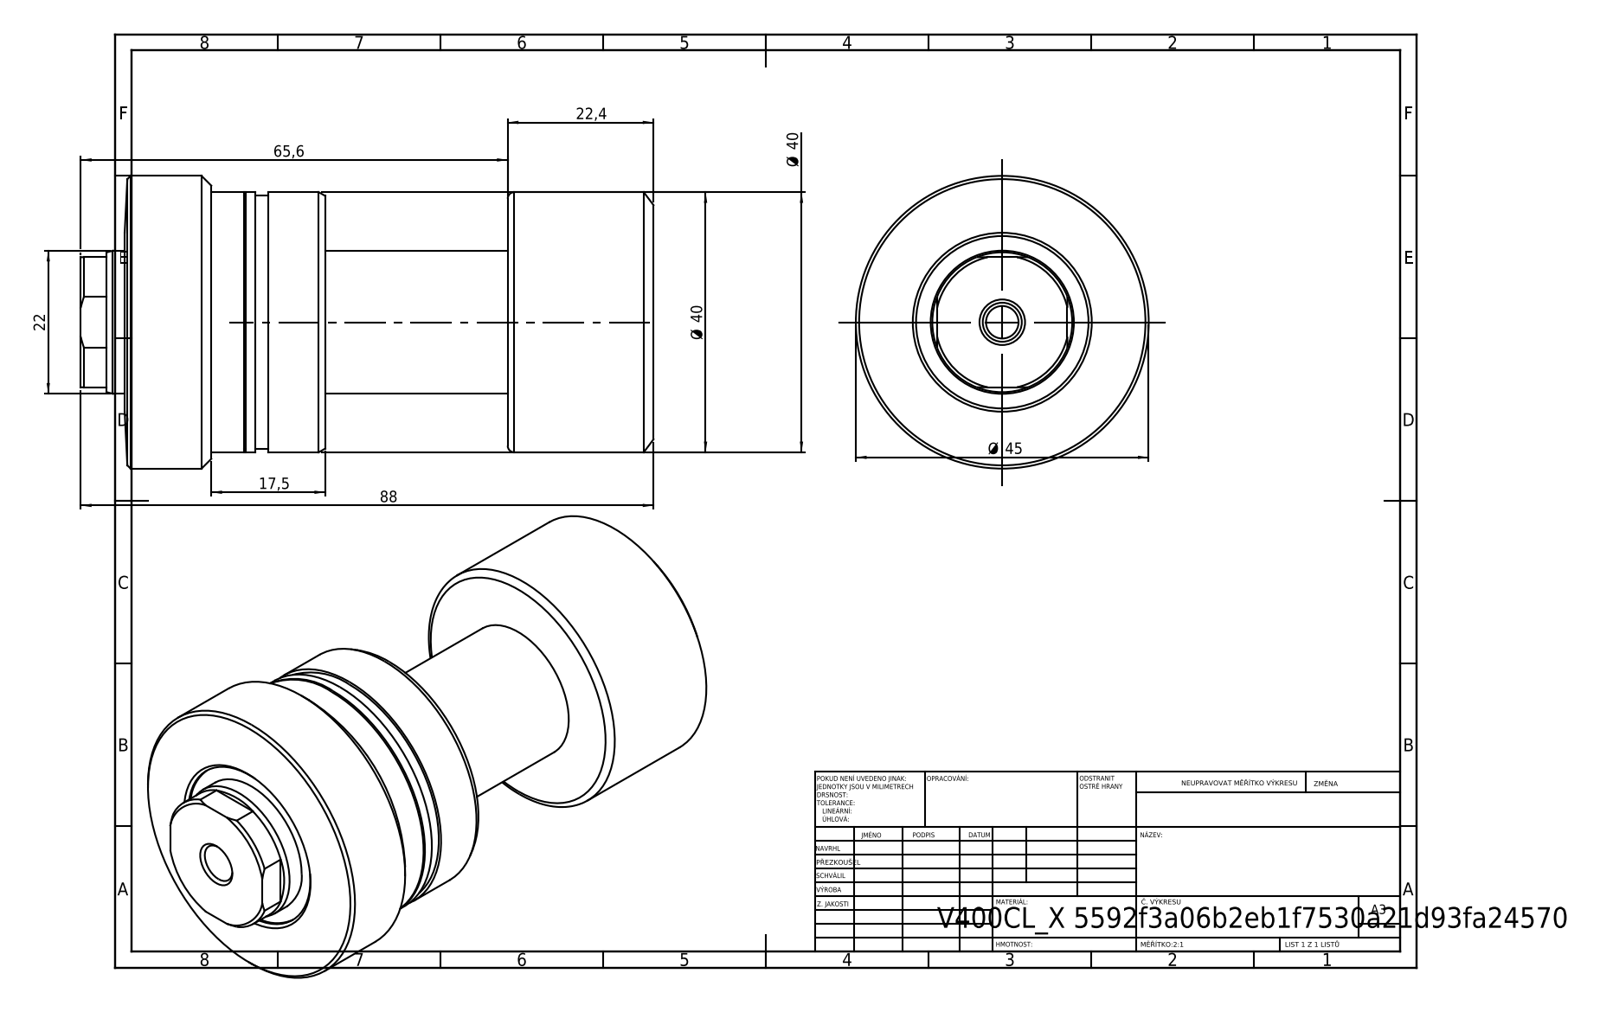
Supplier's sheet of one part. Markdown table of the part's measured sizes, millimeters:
| quantity | value |
| --- | --- |
| part name | V400CL_VC_X; V400CL_PC_X |
| STEP written by | SolidWorks 2019 (CONFIG_CONTROL_DESIGN) |
| units | millimeters |
| bodies | 2 solids, 79 faces (19 planar, 30 cylindrical, 30 other) |
| overall size | 88 × 45 × 45 |
| volume | 82 836 mm³ |
| surface area | 18 587 mm² |
| round holes (diameter × count) | 2.05 × 1, 5 × 1, 6 × 1, 22 × 1, 26.5 × 1 |
| round bosses / shafts (diameter × count) | 45 × 1, 40 × 1, 39 × 1 |
| partial cylindrical surfaces (radius × count) | 10.75 × 1 |
| main face-to-face distances | 22.4, 50.45, 28.05, 88, 65.6, 37.55, 12.5, 17.5, 80.45, 58.05 |
